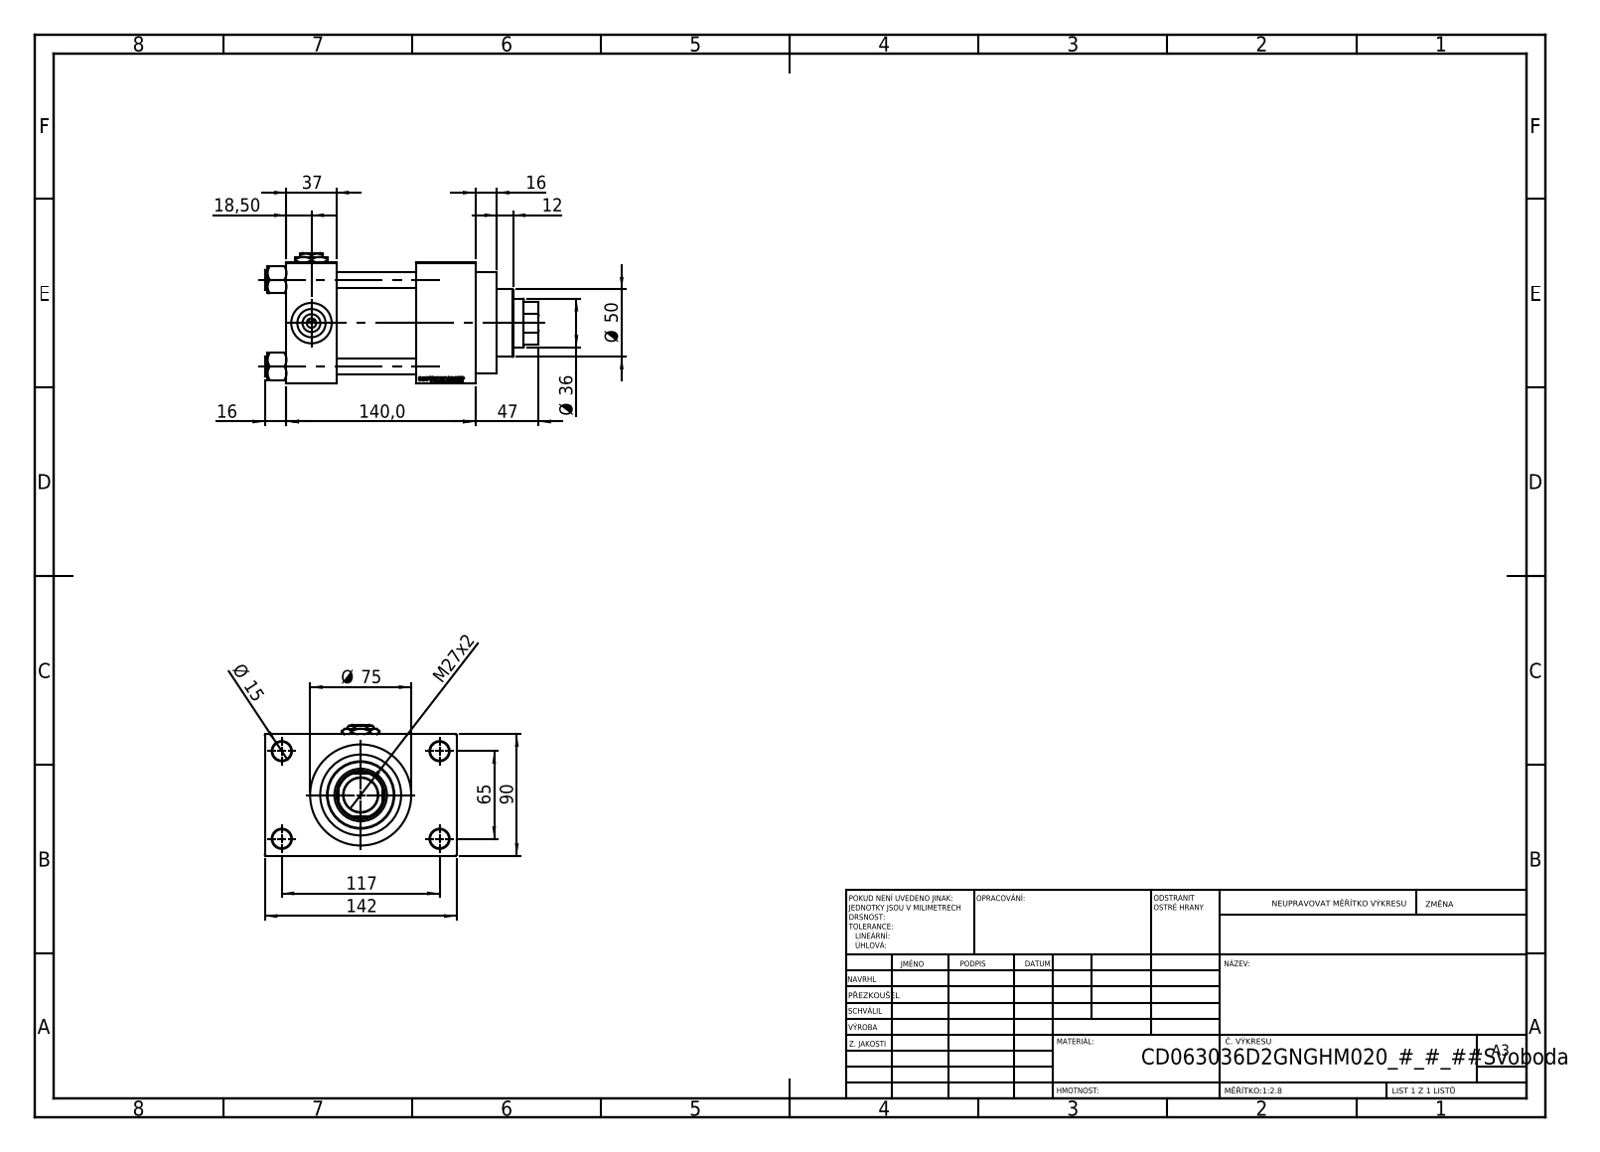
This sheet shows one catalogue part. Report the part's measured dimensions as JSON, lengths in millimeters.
{"part_name": "V215CD_VC_A; Zatka_pro_OIL_PORT; V215CD_D_Body; V215CD_NUT_M5_D (+2 more)", "step_written_by": "SolidWorks 2019 (CONFIG_CONTROL_DESIGN)", "units": "millimeters", "bodies": {"solids": 12, "faces": 1156, "planar": 521, "cylindrical": 95, "other": 540}, "overall_size": [203, 142, 97], "volume_mm3": 1109000, "surface_area_mm2": 208556, "round_holes": [[12, 4], [14, 4], [7, 3], [20.96, 3], [30, 3], [25.5, 1], [36, 1], [39, 1], [50, 1], [60, 1], [63, 1]], "round_bosses_or_shafts": [[15, 4], [75, 1], [69, 1]], "partial_cylinders_radius": [[17.5, 1]], "face_to_face_distances": [90, 59, 37, 96, 140, 103, 44, 116, 26, 142], "hole_center_spacings": [26.35, 45.47, 64.3, 66.92, 69.81, 90.65, 111.34, 65]}
